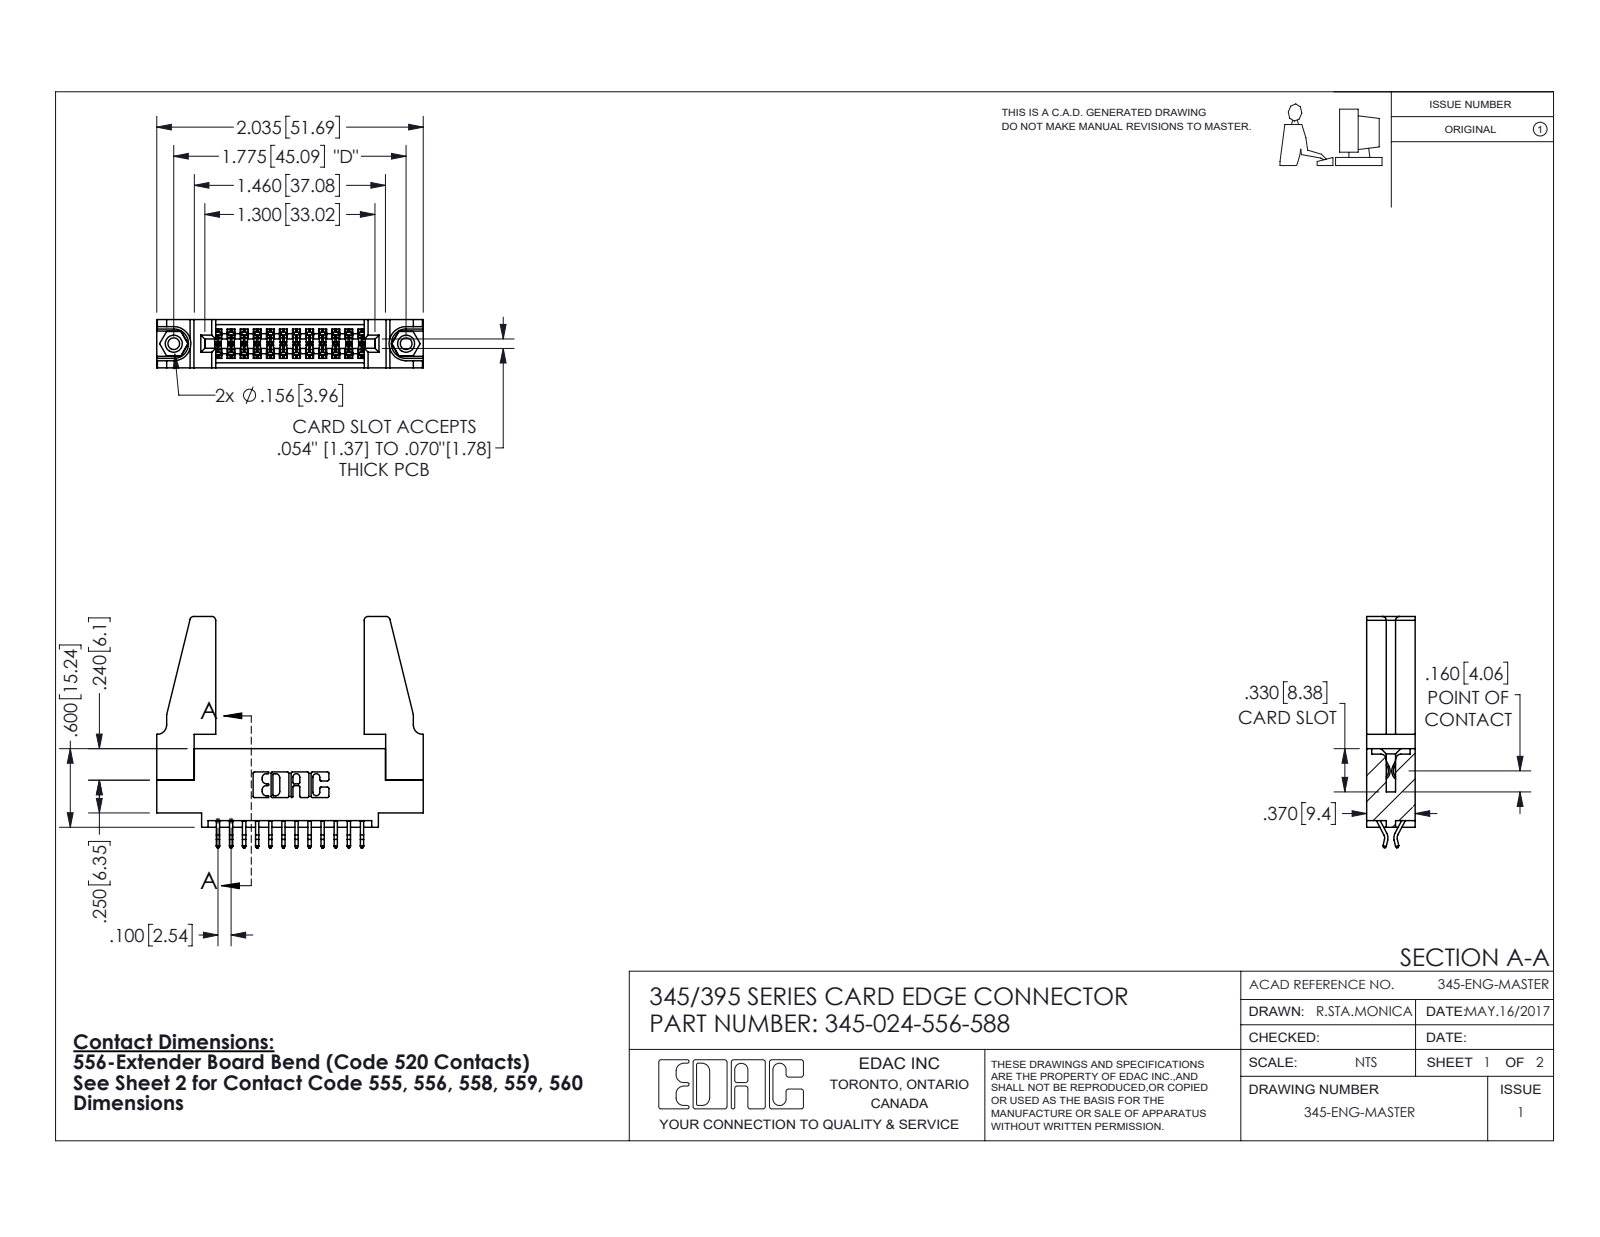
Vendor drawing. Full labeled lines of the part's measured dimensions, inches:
Part name (STEP PRODUCT): 345 Part_0.110 Offset - 0.156 Dia-TH; 345-292-001_556 Tail; 345-220-078_345-220-088; 345-250-001_345-250-001-102 (+1 more)
STEP written by: SolidWorks 2016 (CONFIG_CONTROL_DESIGN)
Units: inches
Bodies: 29 solids, 1598 faces (1044 planar, 538 cylindrical, 16 other)
Overall size (bounding box): 2.036 × 1.767 × 0.37
Volume: 0.484 in³ · Surface area: 14.75 in²
Round holes (diameter × count): ⌀0.089 ×2, ⌀0.125 ×2, ⌀0.156 ×2, ⌀0.064 ×1
Round bosses / shafts (diameter × count): ⌀0.155 ×2
Partial cylindrical surfaces — rounded edges, fillets, slot ends (radius × count): R0.006 ×36, R0.01 ×22, R0.03 ×8, R0.007 ×6, R0.031 ×6, R0.026 ×3, R0.01 ×2, R0.014 ×2
Main face-to-face distances: 0.37, 0.072, 0.298, 0.2, 0.025, 0.098, 0.272, 0.225, 0.148, 0.15
Hole centre spacings: 0.27, 1.543, 1.775
